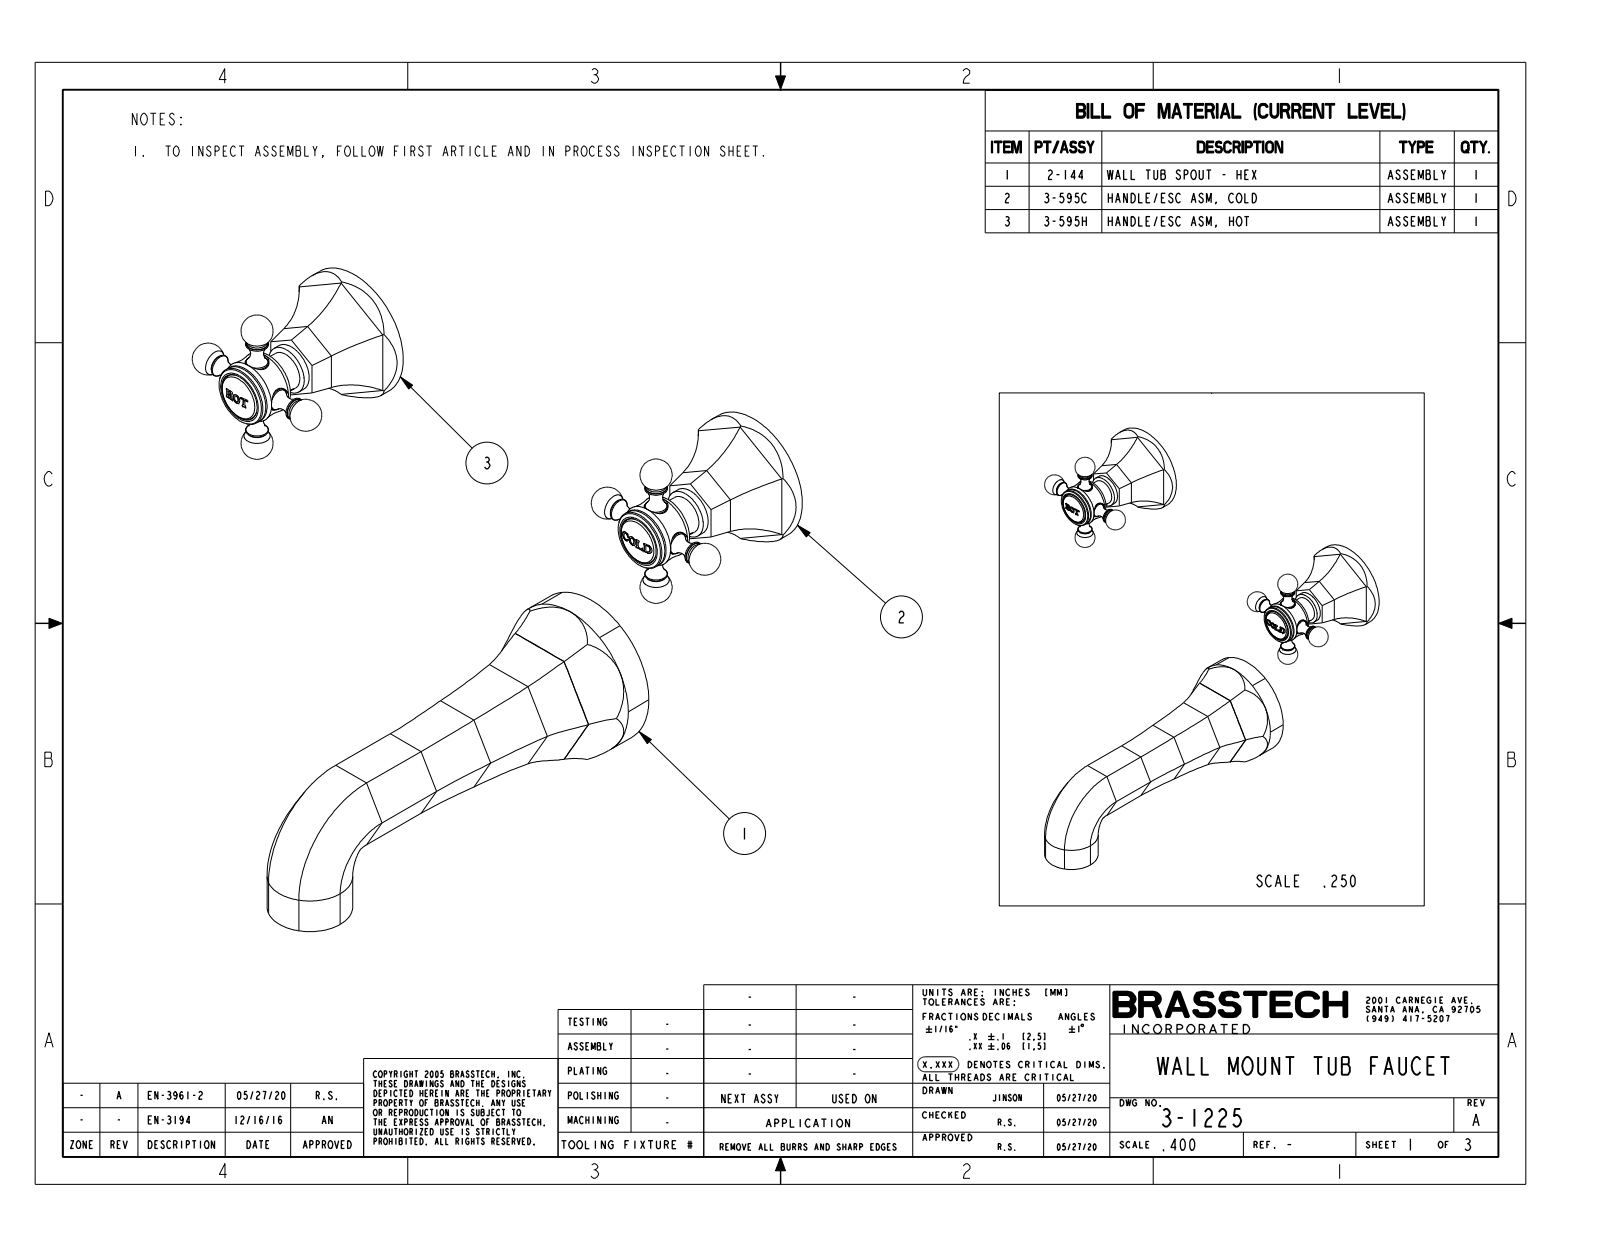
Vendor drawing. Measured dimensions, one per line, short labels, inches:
name: 3-1225_SW0001
written by: CREO PARAMETRIC BY PTC INC, 2018400 (AUTOMOTIVE_DESIGN)
unit: in
bodies: 3 solids, 462 faces (120 planar, 126 cylindrical, 216 other)
size: 10.789 × 9.103 × 7.577
volume: 28.17 in³; area: 101.8 in²
holes: 3× ⌀0.41, 2× ⌀0.855
bosses: 3× ⌀0.392, 2× ⌀2.375, 2× ⌀1.055, 2× ⌀0.86, 2× ⌀0.687, 2× ⌀0.266, 1× ⌀2.8
rounds: 12× R1.541, 7× R0.006, 7× R0.024, 6× R2.125, 5× R0.03, 3× R0.048, 2× R0.018, 2× R0.036
face distances: 1.299, 0.995, 2.294, 3.866, 2.748, 1.527, 7.732, 1.647, 0.12, 5.496
hole spacings: 7.874
